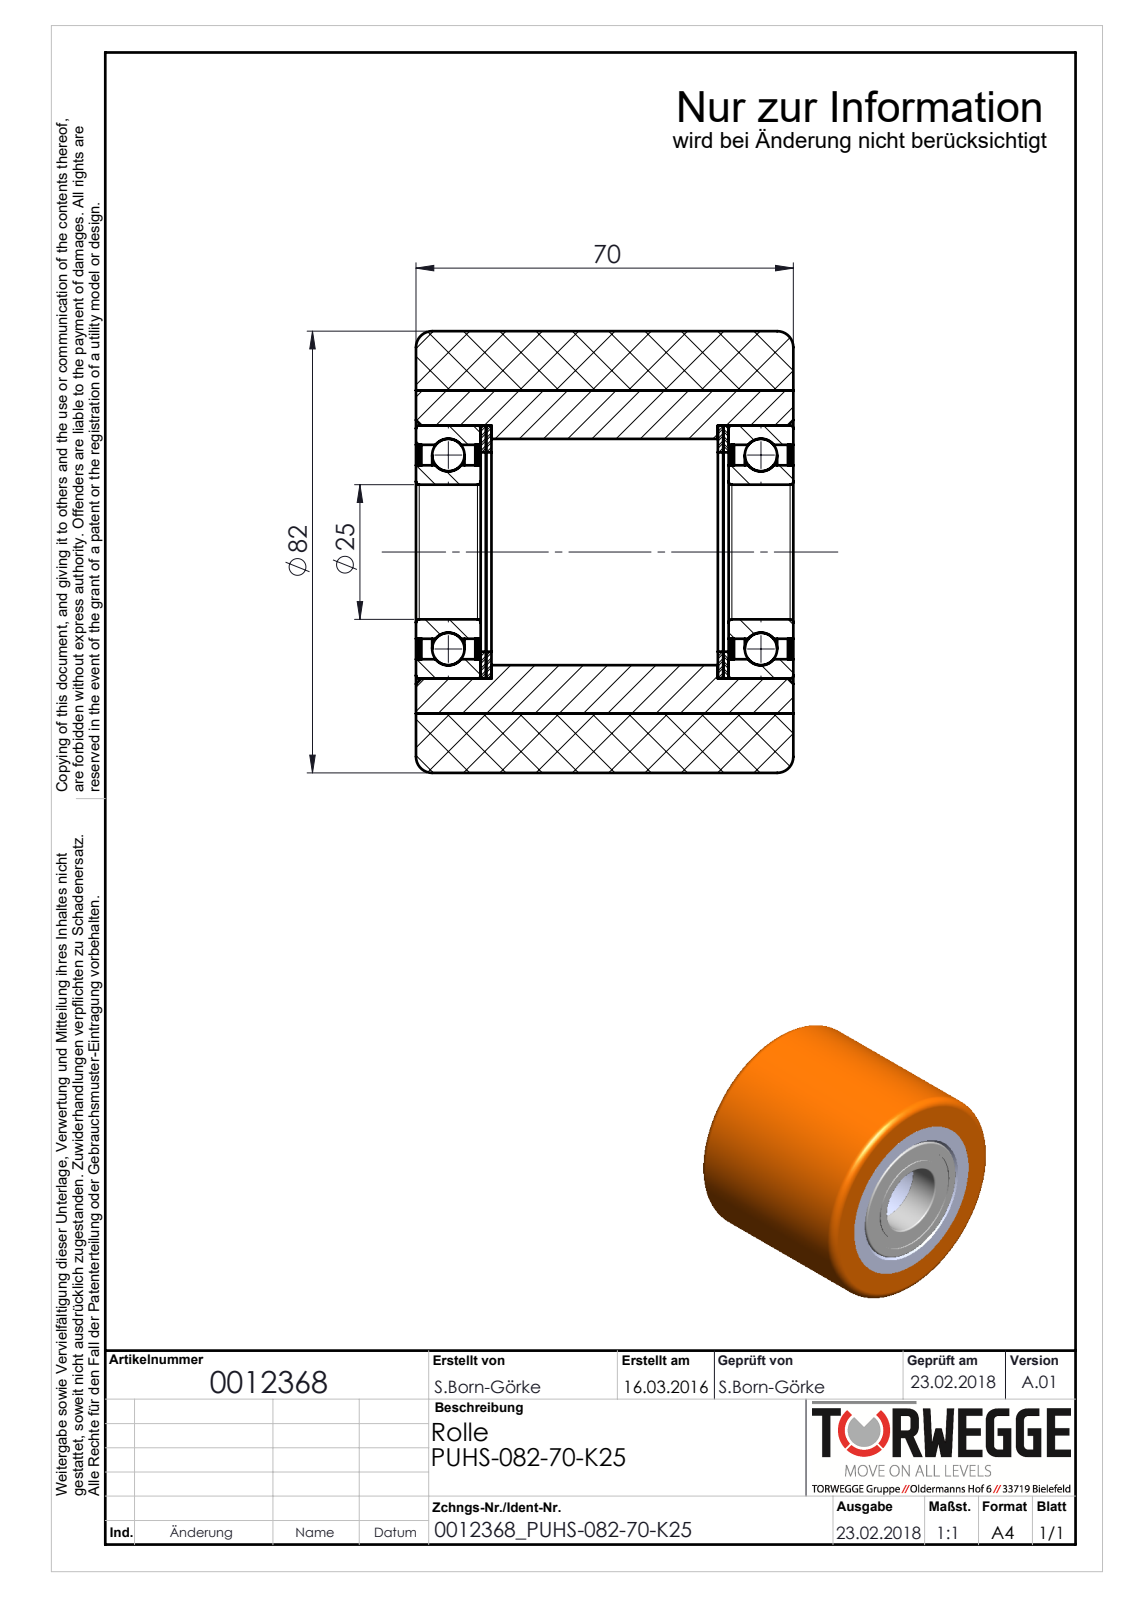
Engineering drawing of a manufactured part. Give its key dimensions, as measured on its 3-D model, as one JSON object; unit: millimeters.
{"part_name": "0012368_PUHS-082-70-K25", "step_written_by": "SolidWorks 2016 (AUTOMOTIVE_DESIGN)", "units": "millimeters", "bodies": {"solids": 16, "faces": 158, "planar": 30, "cylindrical": 68, "other": 60}, "overall_size": [82, 82, 70], "volume_mm3": 289264, "surface_area_mm2": 89617, "round_holes": [[25, 1], [32.2, 1], [37, 1], [39.8, 1], [42, 1], [60, 1]], "round_bosses_or_shafts": [[82, 1], [47, 1]], "face_to_face_distances": [1, 58, 12, 0.5, 13, 57, 45, 70, 44, 56]}
